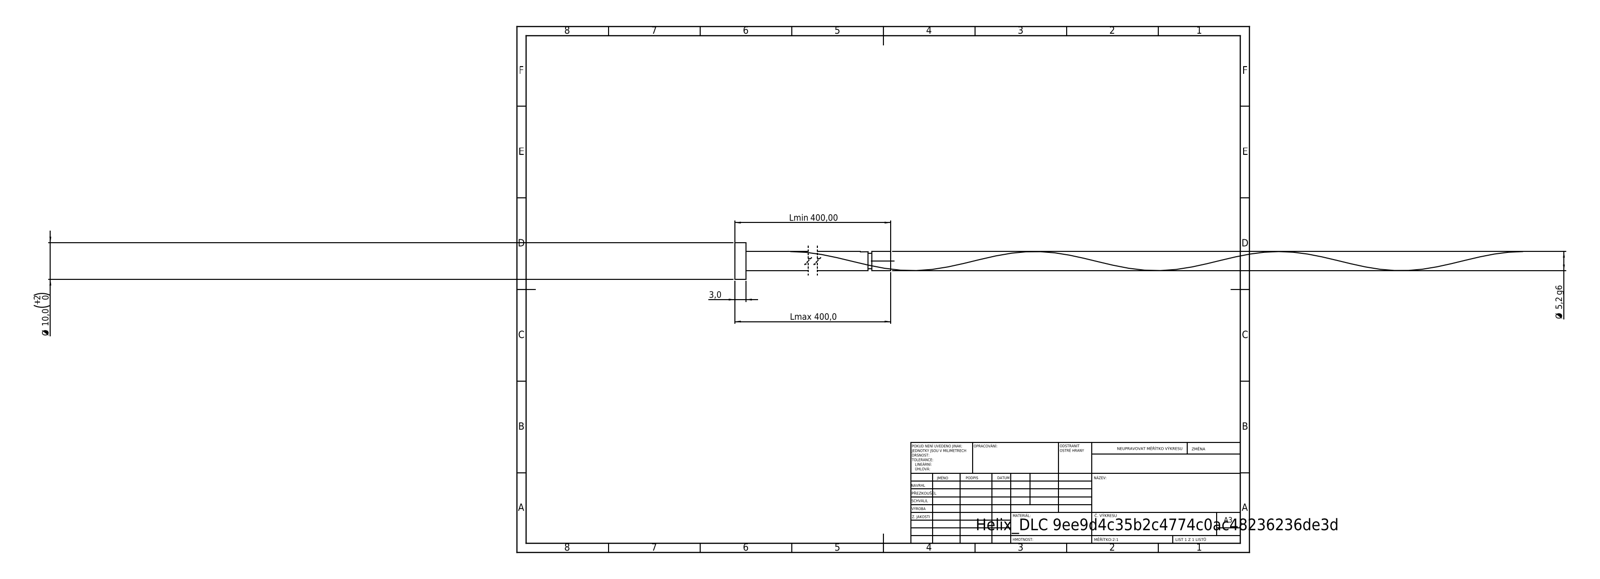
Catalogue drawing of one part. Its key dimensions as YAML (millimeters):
step_written_by: "SolidWorks 2019 (CONFIG_CONTROL_DESIGN)"
units: millimeters
bodies: {solids: 1, faces: 16, planar: 6, cylindrical: 9, other: 1}
overall_size: [400, 10, 10]
volume: 10466
surface_area: 9030
round_bosses_or_shafts:
  - {diameter: 10, count: 1}
  - {diameter: 5.2, count: 1}
  - {diameter: 4.16, count: 1}
face_to_face_distances: [3, 400, 397, 394.9, 391.9, 5.1, 393.86, 390.86, 1.04, 6.14]
